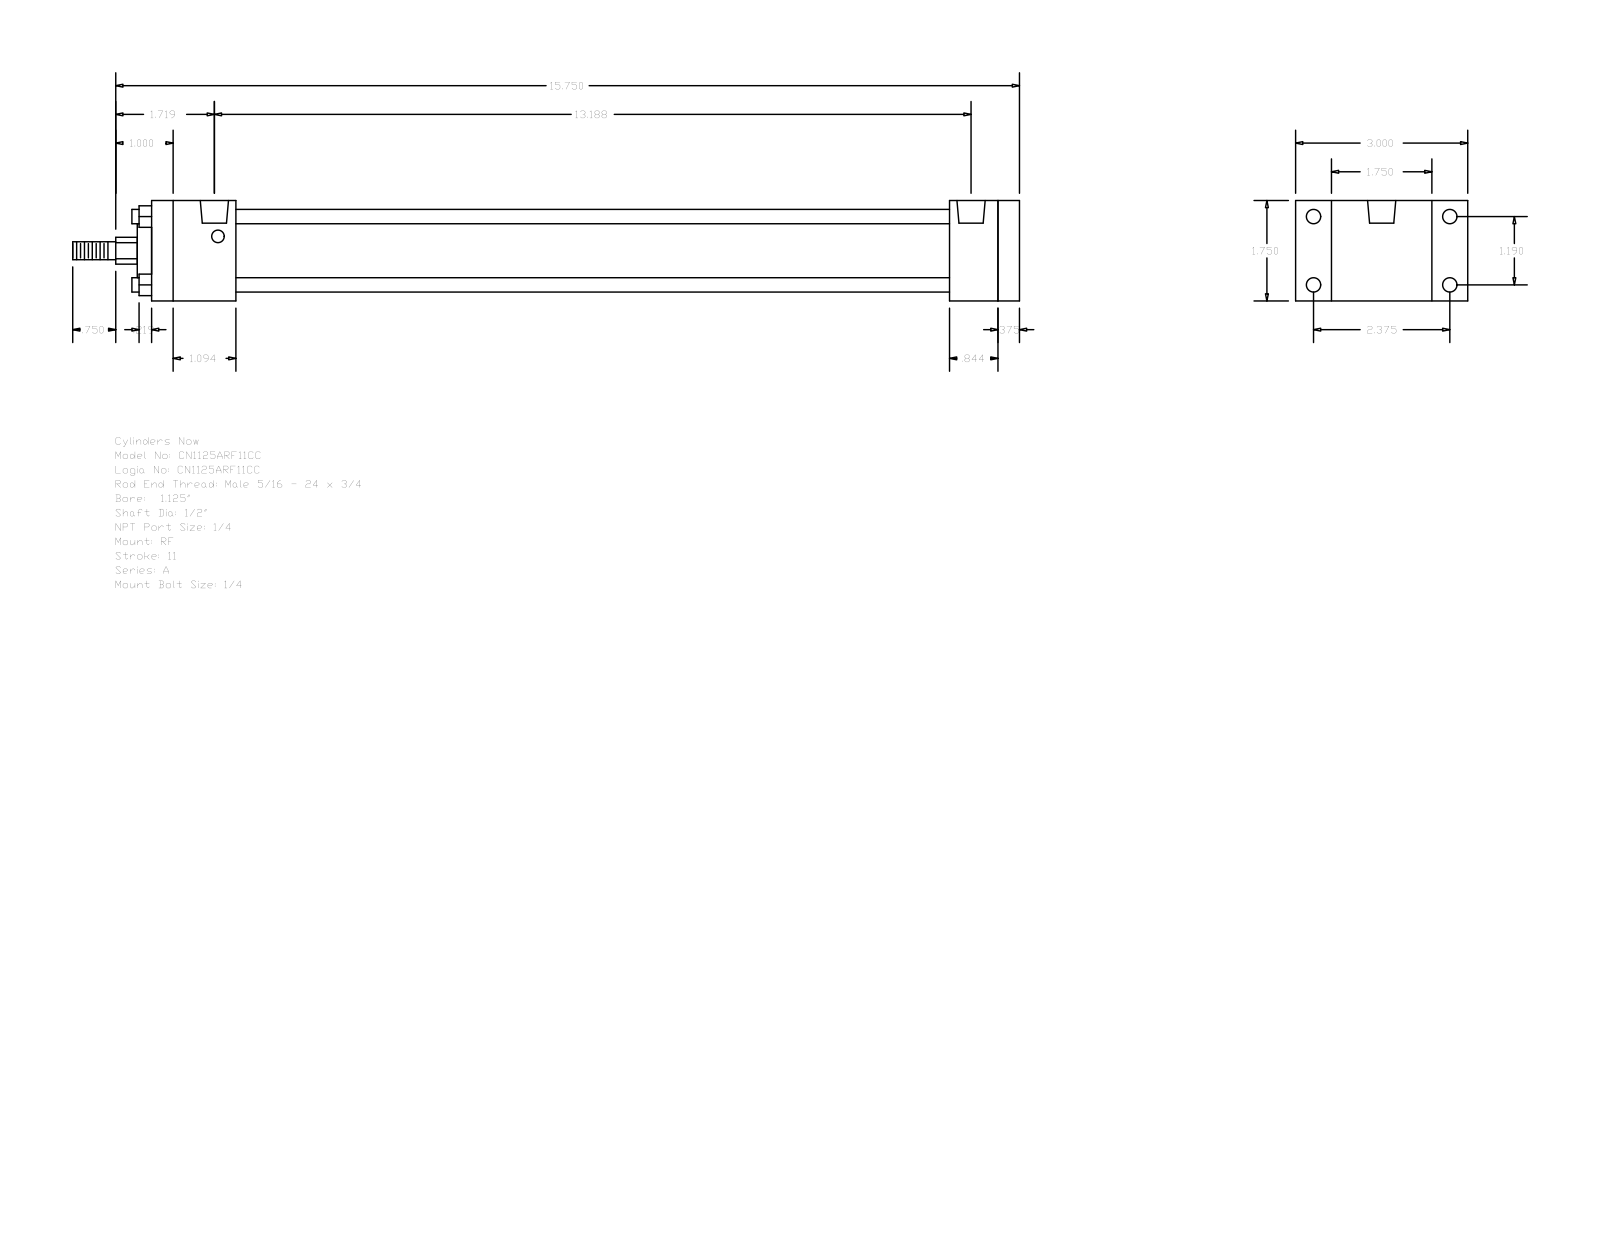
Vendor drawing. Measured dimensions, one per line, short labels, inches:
name: A_RF__0112_0.5
written by: GSSL Pune (CONFIG_CONTROL_DESIGN)
unit: in
bodies: 0 solids, 92 faces (64 planar, 28 cylindrical, 0 other)
size: 16.5 × 3 × 1.75
holes: 4× ⌀0.219, 4× ⌀0.25, 2× ⌀0.492
bosses: 4× ⌀0.25, 1× ⌀1.255, 1× ⌀0.937, 1× ⌀0.5, 1× ⌀0.313
rounds: 1× R0.234
face distances: 1.75, 0.375, 15.125, 14.75, 1.469, 13.906, 12.437, 13.281, 13.656, 0.844
hole spacings: 1.19, 2.375, 2.656, 13.063, 0.062, 0.063, 13.125, 13.125
